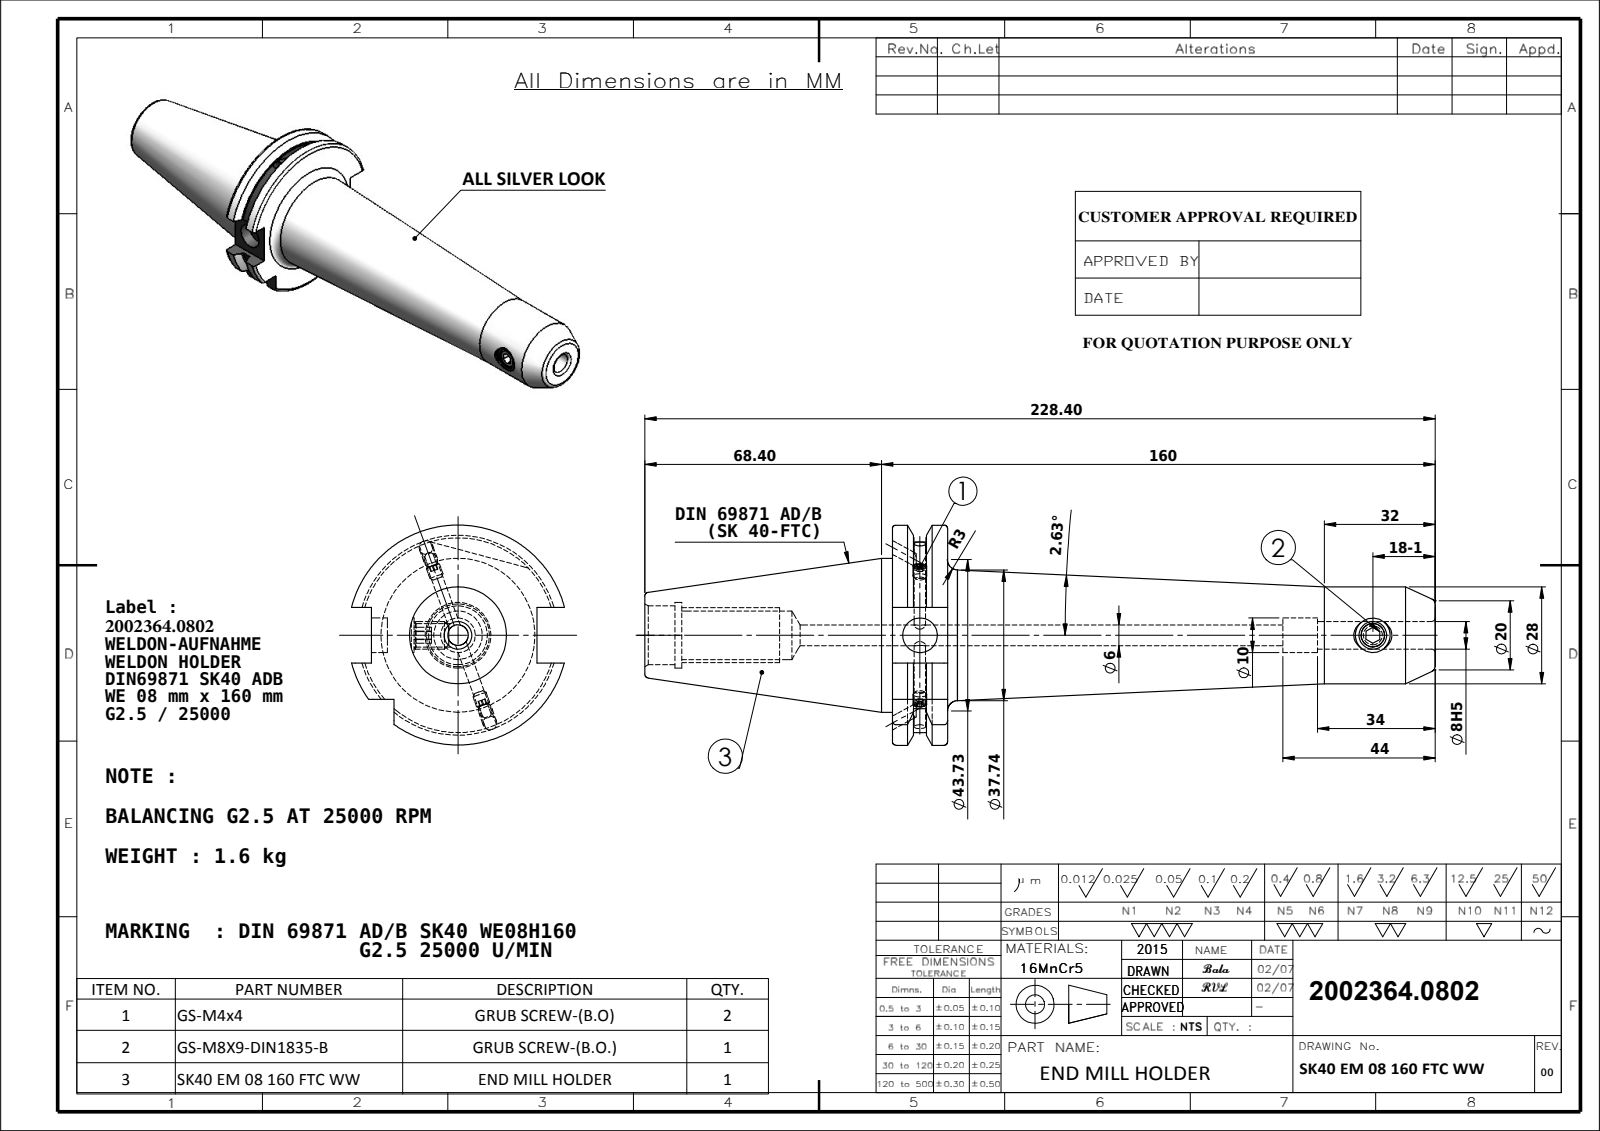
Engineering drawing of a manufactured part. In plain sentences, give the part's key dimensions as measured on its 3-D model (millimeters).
The part is named "Copy of M4X4_DIN 913 - M4 x 4-N; SK40 EM 08 160 FTC WW; M8X10._DIN 913 - M8 x 8-N; 91406-WE708160". Its 3-D file was written by "SolidWorks 2009 (CONFIG_CONTROL_DESIGN)". It is 4 solids with 156 faces: 58 planar, 44 cylindrical and 54 other. Overall it measures 228.4 by 63.55 by 61.48 millimeters. Its volume is 210 989 cubic millimeters and its surface area 37 283 square millimeters. Round holes: 3 of diameter 10, 1 of diameter 3.3, 1 of diameter 6, 1 of diameter 6.8, 1 of diameter 8, 1 of diameter 14, 1 of diameter 17, 1 of diameter 19. Round bosses or shafts: 2 of diameter 4, 1 of diameter 44.45, 1 of diameter 28, 1 of diameter 8. Partial cylindrical surfaces (rounded edges, fillets, slot ends): 1 of radius 28.12, 1 of radius 31.77. The main face-to-face distances are 15.9, 156.8, 140.9, 16.1, 47.8, 71.6, 87.5, 228.4, 10.7, 60.9. The hole center spacings are 130.85.
